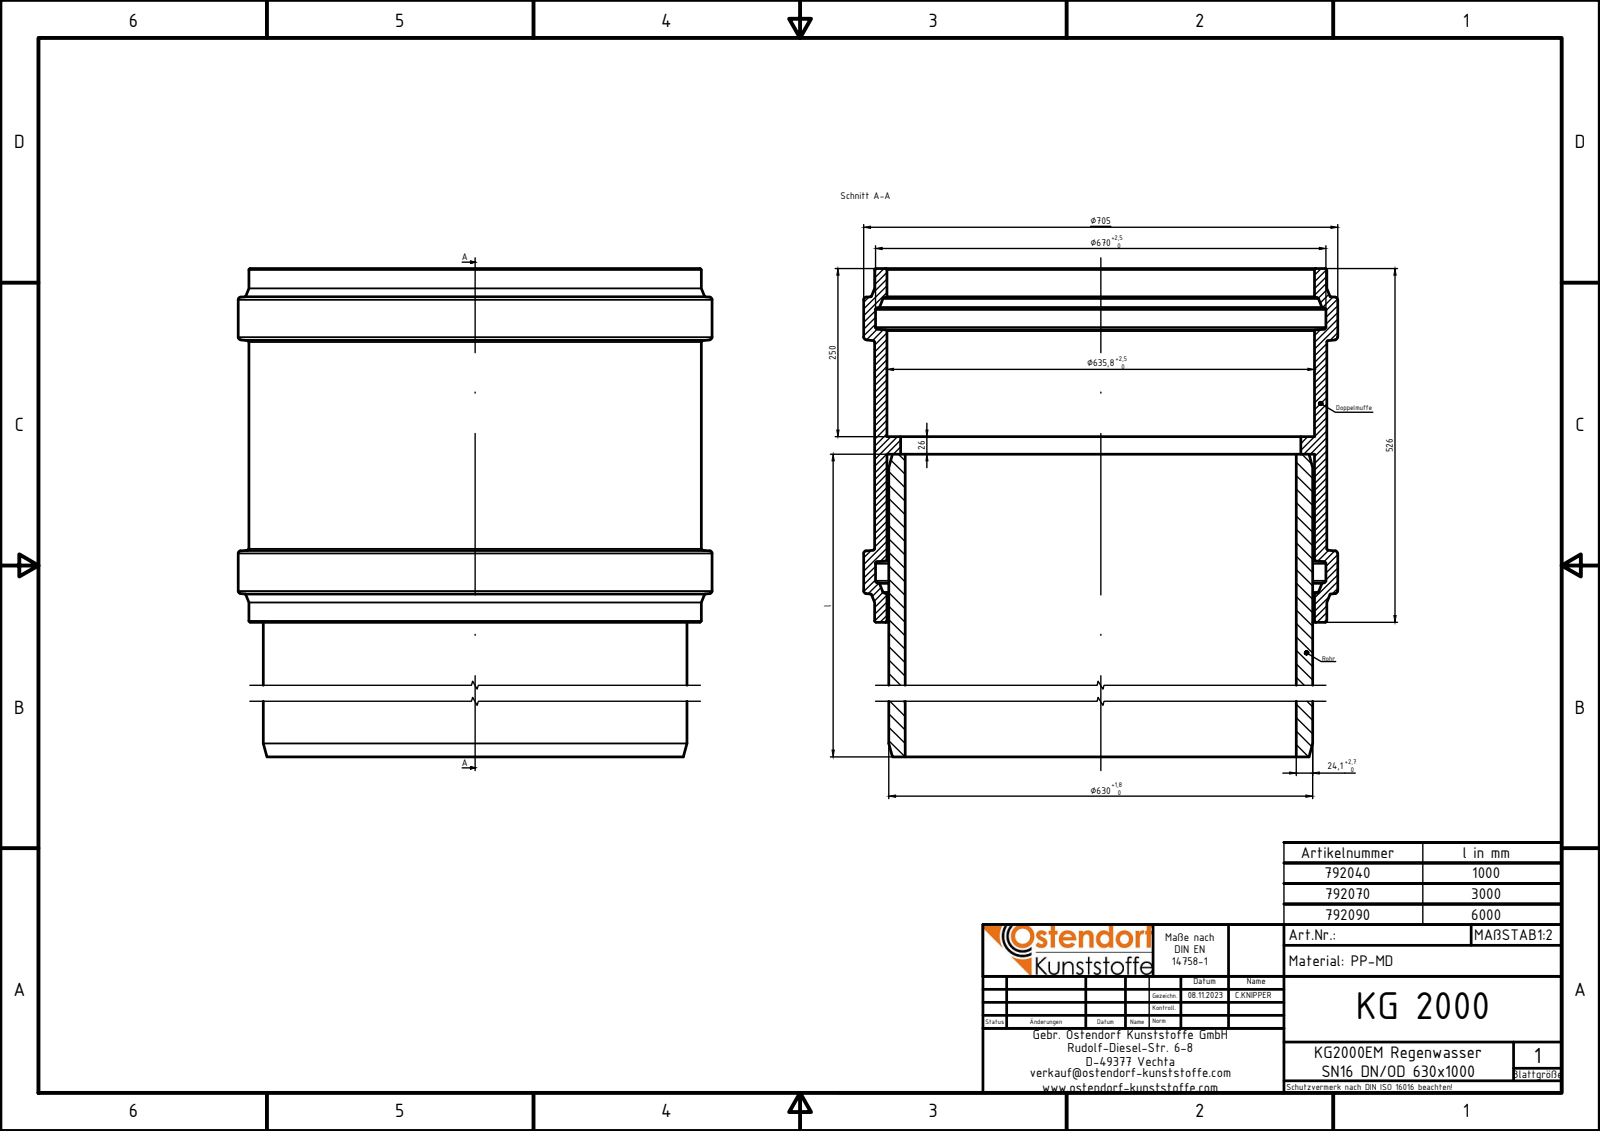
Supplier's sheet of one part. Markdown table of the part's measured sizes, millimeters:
| quantity | value |
| --- | --- |
| part name | 792040z |
| STEP written by | Autodesk Inventor 2024 (AUTOMOTIVE_DESIGN) |
| units | millimeters |
| bodies | 1 solid, 60 faces (6 planar, 14 cylindrical, 40 other) |
| overall size | 1276 × 704.8 × 704.8 |
| volume | 68 410 000 mm³ |
| surface area | 6 353 000 mm² |
| round holes (diameter × count) | 581.8 × 1, 594.8 × 1, 635.8 × 1, 670 × 1 |
| round bosses / shafts (diameter × count) | 704.8 × 1, 672.6 × 1, 630 × 1 |
| main face-to-face distances | 276, 250, 1026, 750, 1276, 526, 1000, 26 |
